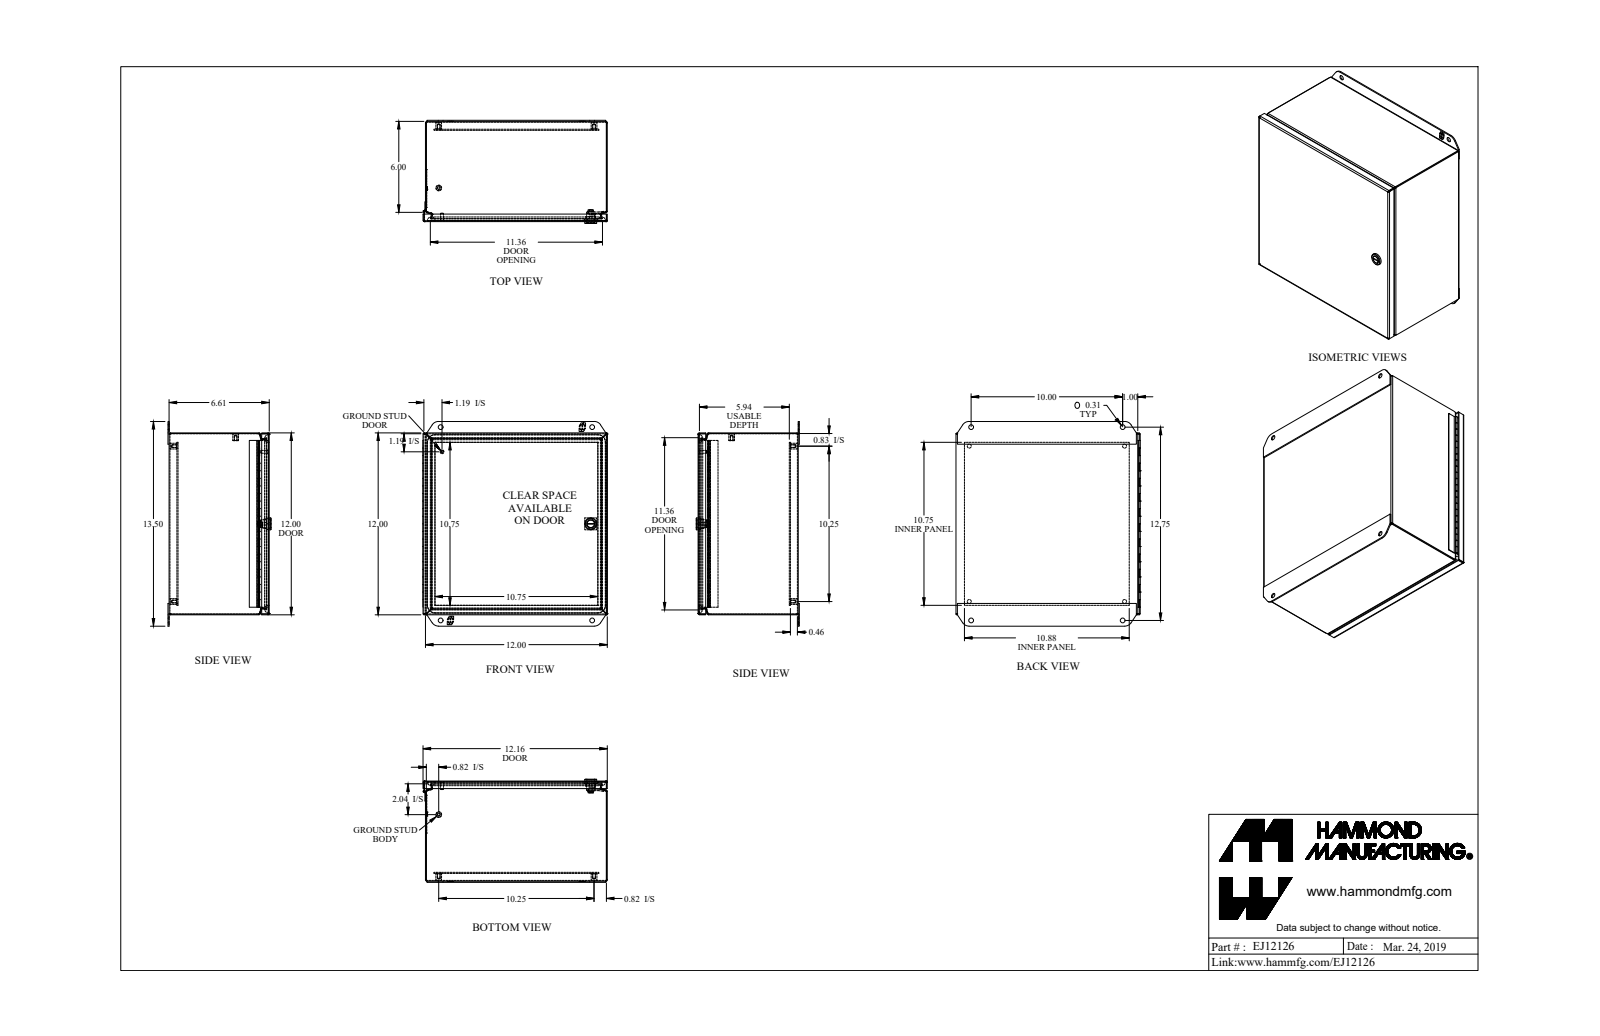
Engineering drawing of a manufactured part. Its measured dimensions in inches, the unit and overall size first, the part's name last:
Units: inches
Overall size (bounding box): 13.5 × 12.165 × 6.805
Round holes (diameter × count): ⌀0.156 ×5, ⌀0.265 ×4, ⌀0.313 ×4, ⌀0.05 ×1, ⌀0.516 ×1
Round bosses / shafts (diameter × count): ⌀0.375 ×5, ⌀0.788 ×1, ⌀0.535 ×1, ⌀0.496 ×1, ⌀0.435 ×1, ⌀0.25 ×1, ⌀0.188 ×1, ⌀0.1 ×1
Partial cylindrical surfaces — rounded edges, fillets, slot ends (radius × count): R0.029 ×16, R0.086 ×16, R0.281 ×10, R0.25 ×4, R0.499 ×4, R0.5 ×4, R0.06 ×2, R0.539 ×2
Main face-to-face distances: 0.057, 6.554, 11.943, 0.072, 0.589, 12, 11.886, 6.611, 6.497, 0.46
Hole centre spacings: 10.25, 5.13, 10.202, 14.496, 15.322, 1.256, 1.256, 11.501
Volume: 51.81 in³ · Surface area: 1 711 in²
Bodies: 16 solids, 707 faces (393 planar, 222 cylindrical, 92 other)
Part name (STEP PRODUCT): EJ12126_Default
STEP written by: SolidWorks 2019 (CONFIG_CONTROL_DESIGN)
